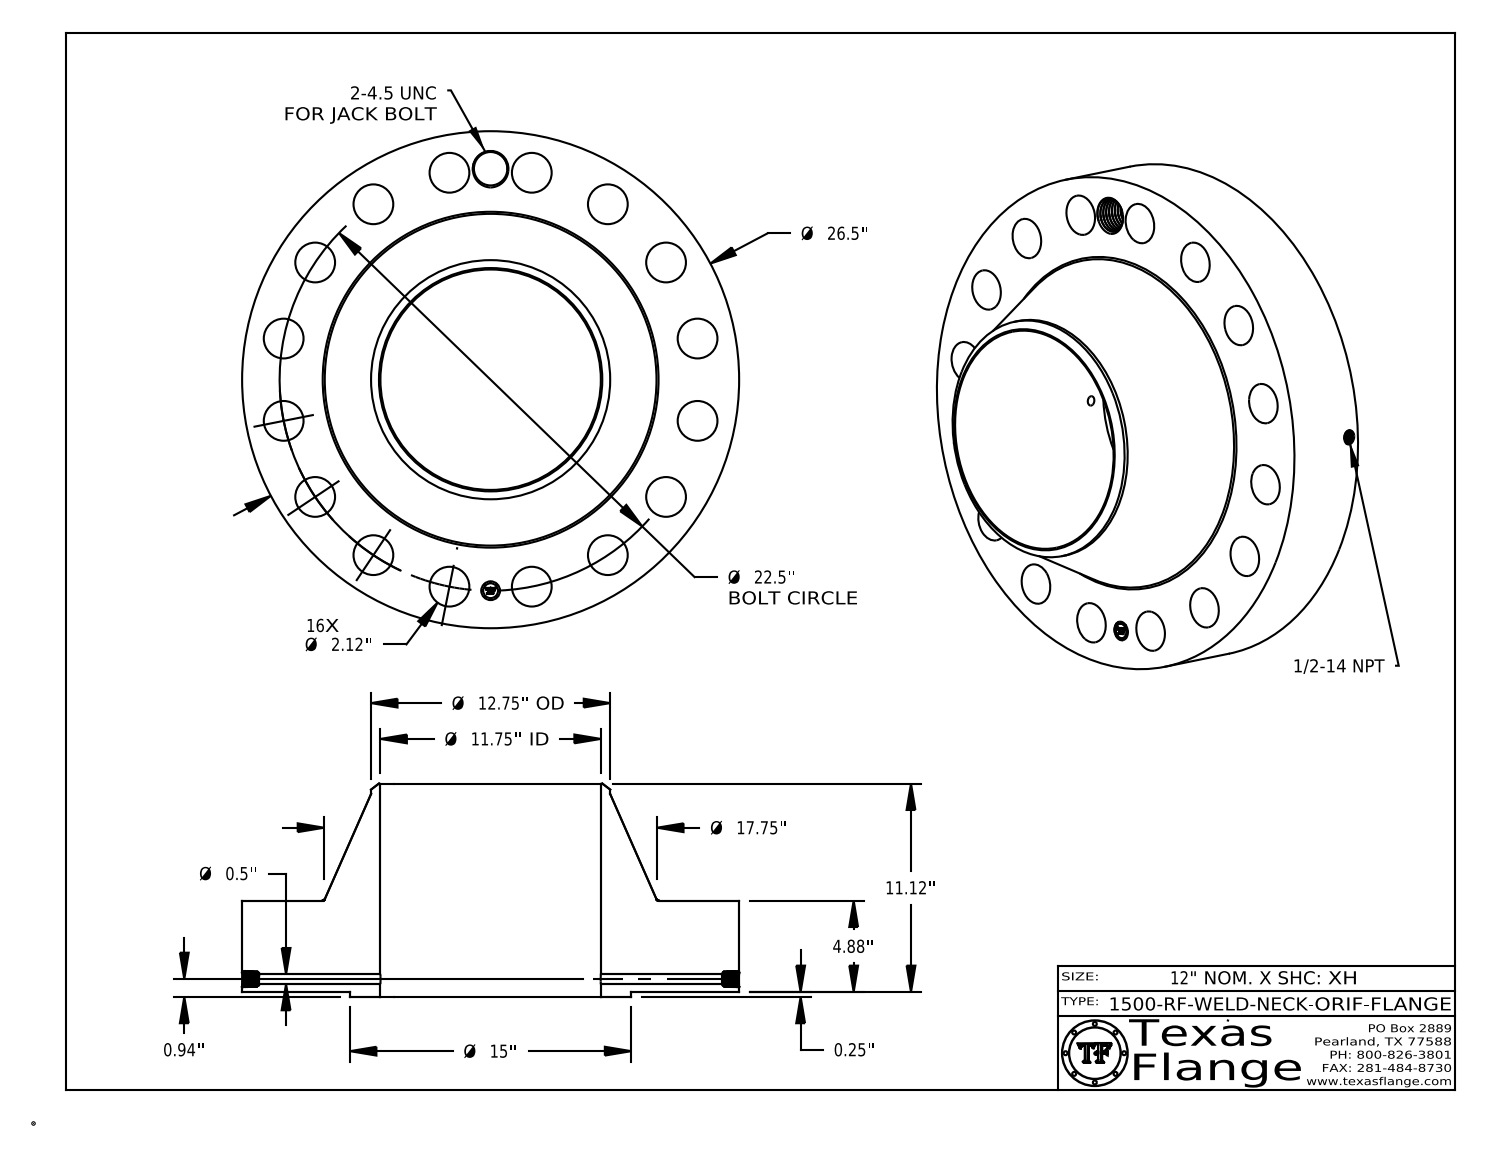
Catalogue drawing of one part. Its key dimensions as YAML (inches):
part_name: "1500-RF-WELD-NECK"
step_written_by: "CATIA V5 STEP AP214 (AUTOMOTIVE_DESIGN)"
units: inches
bodies: {solids: 1, faces: 827, planar: 369, cylindrical: 124, other: 334}
overall_size: [26.5, 26.5, 11.37]
volume: 2326
surface_area: 2383
round_holes:
  - {diameter: 2.12, count: 16}
  - {diameter: 0.5, count: 1}
  - {diameter: 0.672, count: 1}
  - {diameter: 1, count: 1}
  - {diameter: 1.781, count: 1}
  - {diameter: 11.75, count: 1}
round_bosses_or_shafts:
  - {diameter: 0.061, count: 8}
  - {diameter: 26.5, count: 1}
  - {diameter: 15, count: 1}
  - {diameter: 12.75, count: 1}
  - {diameter: 0.788, count: 1}
face_to_face_distances: [4.88, 0.25, 5.13, 11.37, 11.12, 6.24, 5.115, 4.865, 0.015, 6.255]
hole_center_spacings: [11.25, 8.61, 15.91, 20.787, 12.5, 18.708, 22.068, 4.389]
